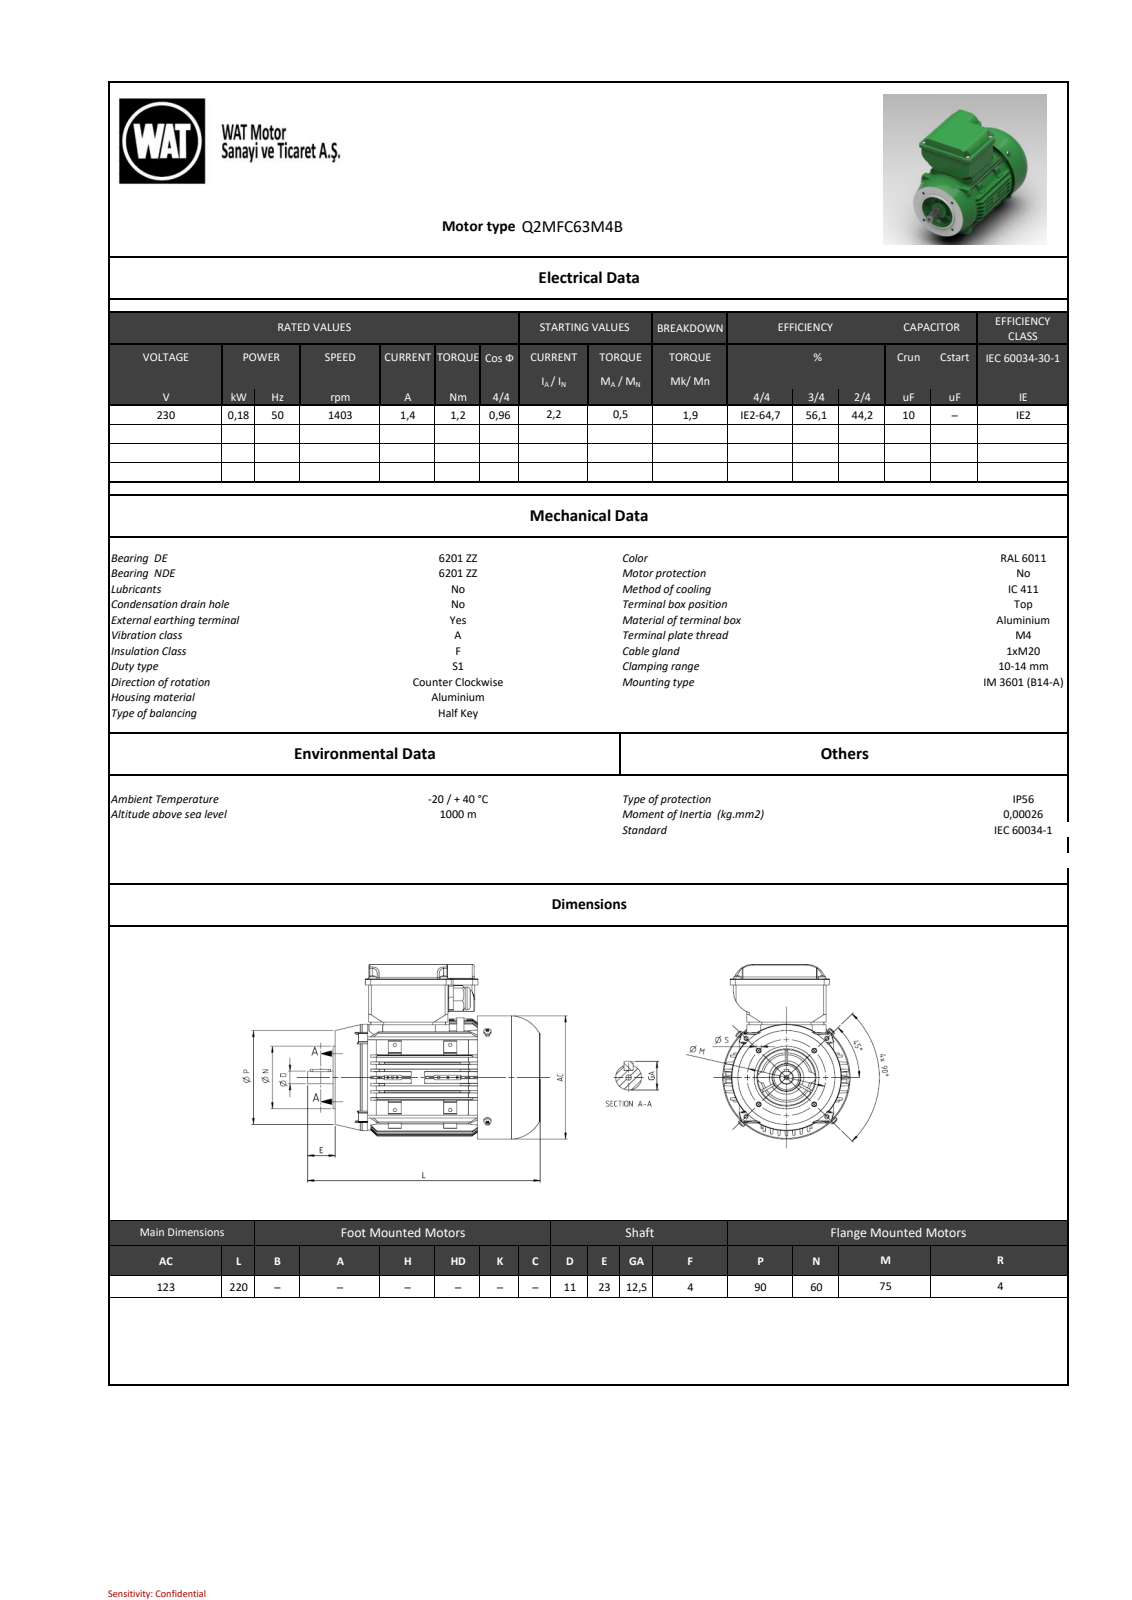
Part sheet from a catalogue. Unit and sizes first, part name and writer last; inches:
Units: inches
Overall size (bounding box): 8.641 × 7.087 × 4.843
Round holes (diameter × count): ⌀0.144 ×10, ⌀0.13 ×9, ⌀0.177 ×8, ⌀0.098 ×6, ⌀0.138 ×4, ⌀0.15 ×4, ⌀0.183 ×4, ⌀0.189 ×4, ⌀0.118 ×3, ⌀0.197 ×1, ⌀0.315 ×1, ⌀0.402 ×1
Round bosses / shafts (diameter × count): ⌀0.315 ×8, ⌀0.157 ×8, ⌀0.118 ×8, ⌀4.843 ×1, ⌀4.764 ×1, ⌀3.898 ×1, ⌀2.756 ×1, ⌀2.362 ×1
Partial cylindrical surfaces — rounded edges, fillets, slot ends (radius × count): R0.02 ×210, R0.039 ×82, R0.079 ×58, R0.098 ×20, R0.157 ×11, R0.197 ×10, R0.118 ×9, R0.217 ×9
Main face-to-face distances: 0.118, 0.059, 0.177, 0.276, 1.101, 0.276, 0.098, 0.157, 0.039, 1.104
Hole centre spacings: 3.031, 2.165, 2.603, 2.144, 1.476, 2.126, 2.48, 2.634
Volume: 33.46 in³ · Surface area: 619.1 in²
Bodies: 34 solids, 2043 faces (1089 planar, 725 cylindrical, 229 other)
Part name (STEP PRODUCT): BY6434017xx_004-TK_QM63-80; BY6424130xx_004-TKK_QM63-80; BY6424111xx_004-MOTOR_KAPAGI_QS63FC_ISLEME; BY6423003xx_006-FAN_KAPAGI_QS63 (+7 more)
STEP written by: SIEMENS PLM Software NX2206.8101 (AUTOMOTIVE_DESIGN)
